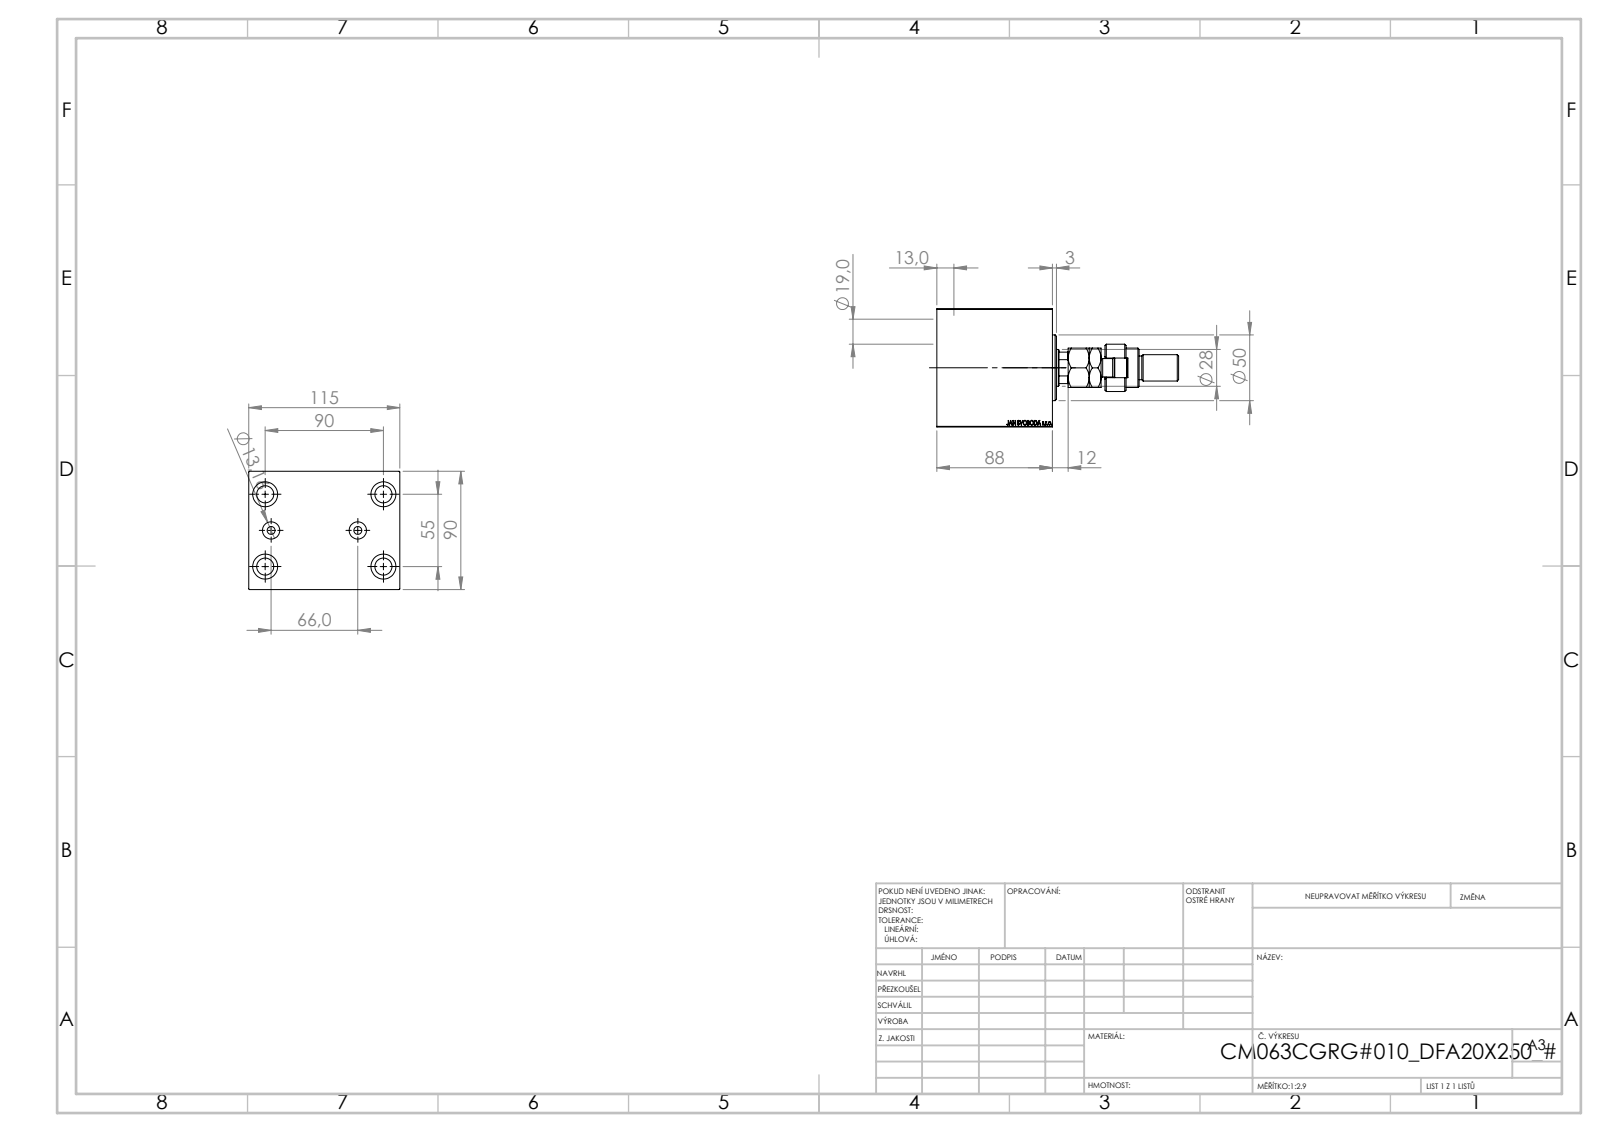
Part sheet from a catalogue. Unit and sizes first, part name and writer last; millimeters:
Units: millimetres
Overall size (bounding box): 185.5 × 115 × 90
Round holes (diameter × count): ⌀13 ×4, ⌀19 ×4, ⌀6 ×2, ⌀13.16 ×2, ⌀18.5 ×1, ⌀28 ×1, ⌀31.5 ×1, ⌀63 ×1, ⌀65 ×1, ⌀72 ×1
Round bosses / shafts (diameter × count): ⌀50 ×1, ⌀36 ×1, ⌀30 ×1, ⌀22 ×1, ⌀20 ×1, ⌀18 ×1, ⌀14 ×1
Partial cylindrical surfaces — rounded edges, fillets, slot ends (radius × count): R7.5 ×1, R12 ×1, R13.5 ×1
Main face-to-face distances: 90, 115, 88, 10, 46, 42, 78, 5, 32, 20
Hole centre spacings: 30, 52.74, 82.71, 33, 55, 90, 105.48, 66
Volume: 869 868 mm³ · Surface area: 121 869 mm²
Bodies: 5 solids, 946 faces (437 planar, 71 cylindrical, 438 other)
Part name (STEP PRODUCT): V450CM_C_Body; MFA; V450CM_VC_B; V450CM_C_VCP (+1 more)
STEP written by: SolidWorks 2019 (CONFIG_CONTROL_DESIGN)
